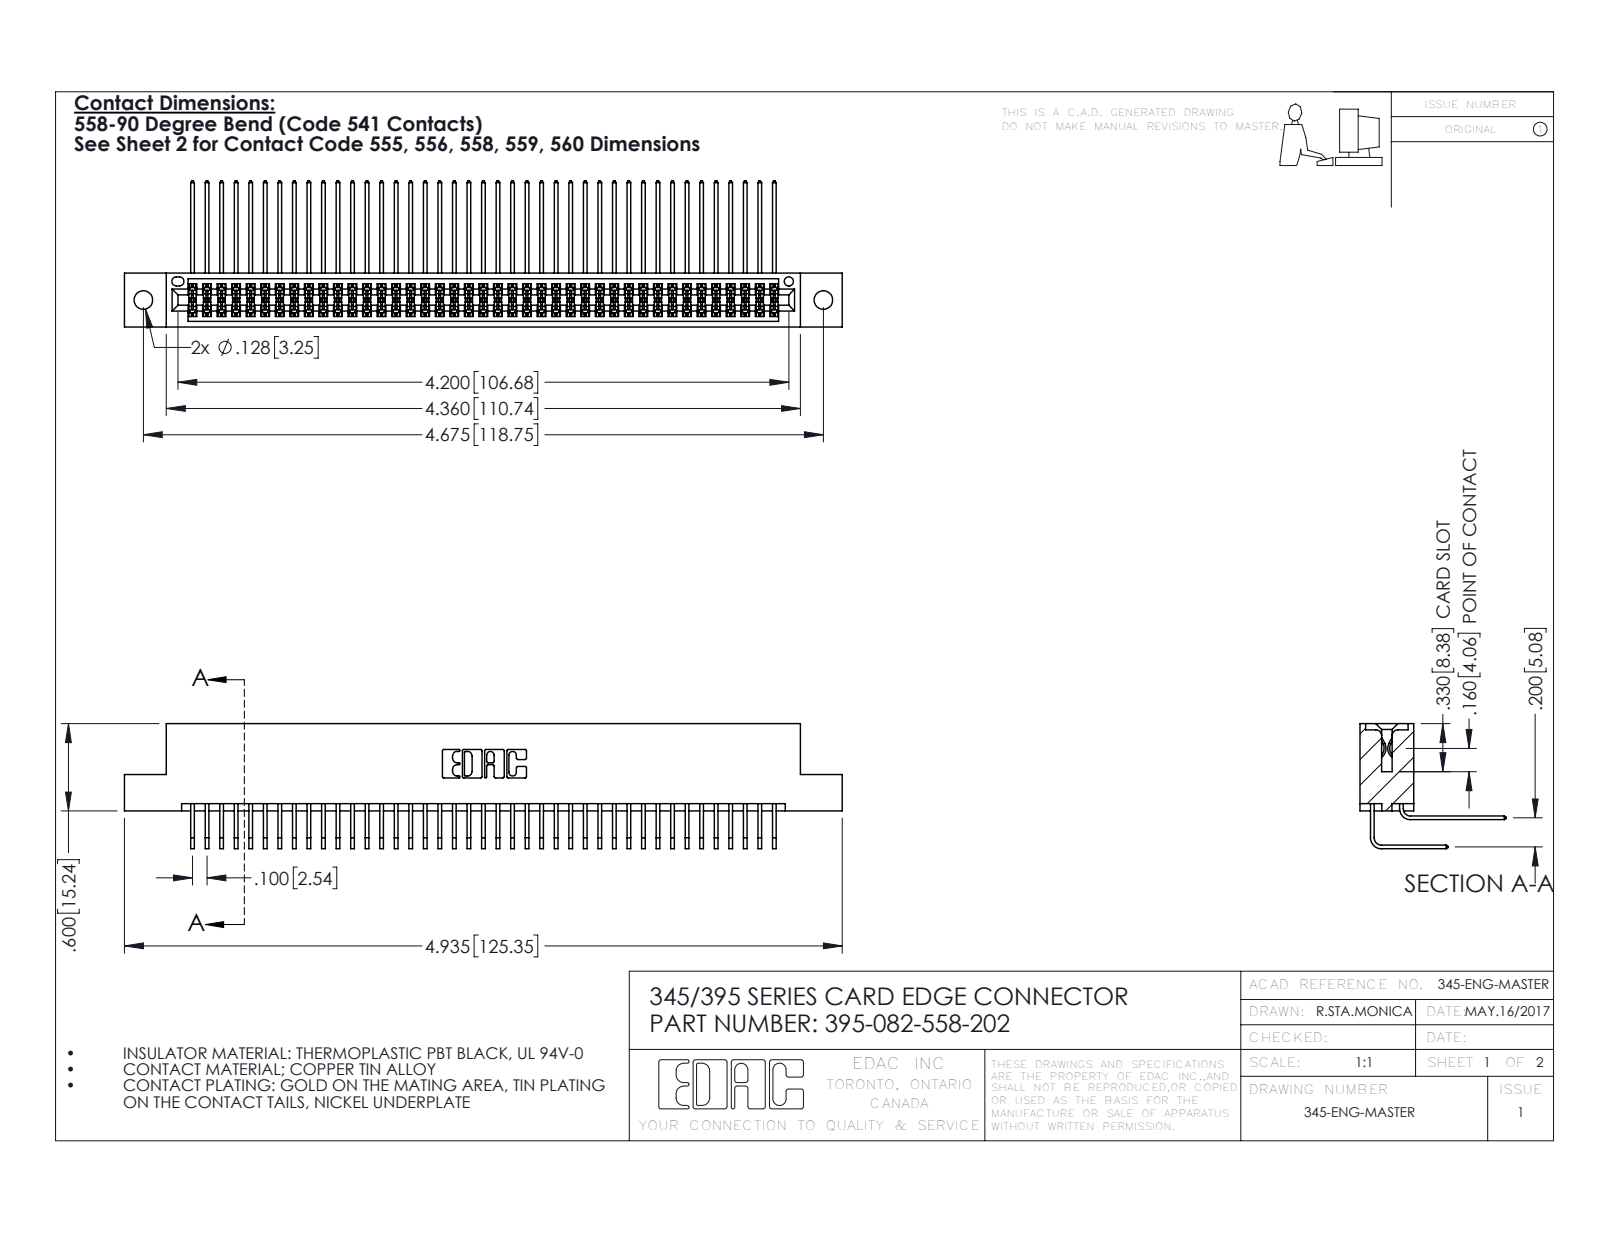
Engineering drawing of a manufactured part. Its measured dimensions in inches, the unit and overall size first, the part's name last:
Units: inches
Overall size (bounding box): 4.935 × 1.005 × 0.859
Round holes (diameter × count): ⌀0.128 ×2, ⌀0.064 ×1
Partial cylindrical surfaces — rounded edges, fillets, slot ends (radius × count): R0.006 ×124, R0.01 ×22, R0.007 ×6, R0.031 ×6, R0.026 ×3, R0.014 ×2, R0.019 ×2, R0.022 ×2
Main face-to-face distances: 0.072, 0.298, 0.2, 0.37, 0.098, 0.272, 0.025, 0.225, 0.025, 0.175
Hole centre spacings: 0.27, 4.439, 4.675
Volume: 0.769 in³ · Surface area: 31.87 in²
Bodies: 83 solids, 4390 faces (2950 planar, 1440 cylindrical, 0 other)
Part name (STEP PRODUCT): 345 Part_Flush Mounting Lugs - 0.128 Dia; 345-292-001_558 Tail - 2; 395-082-558-202; 345-292-001_558 559 Tail - 1
STEP written by: SolidWorks 2016 (CONFIG_CONTROL_DESIGN)
